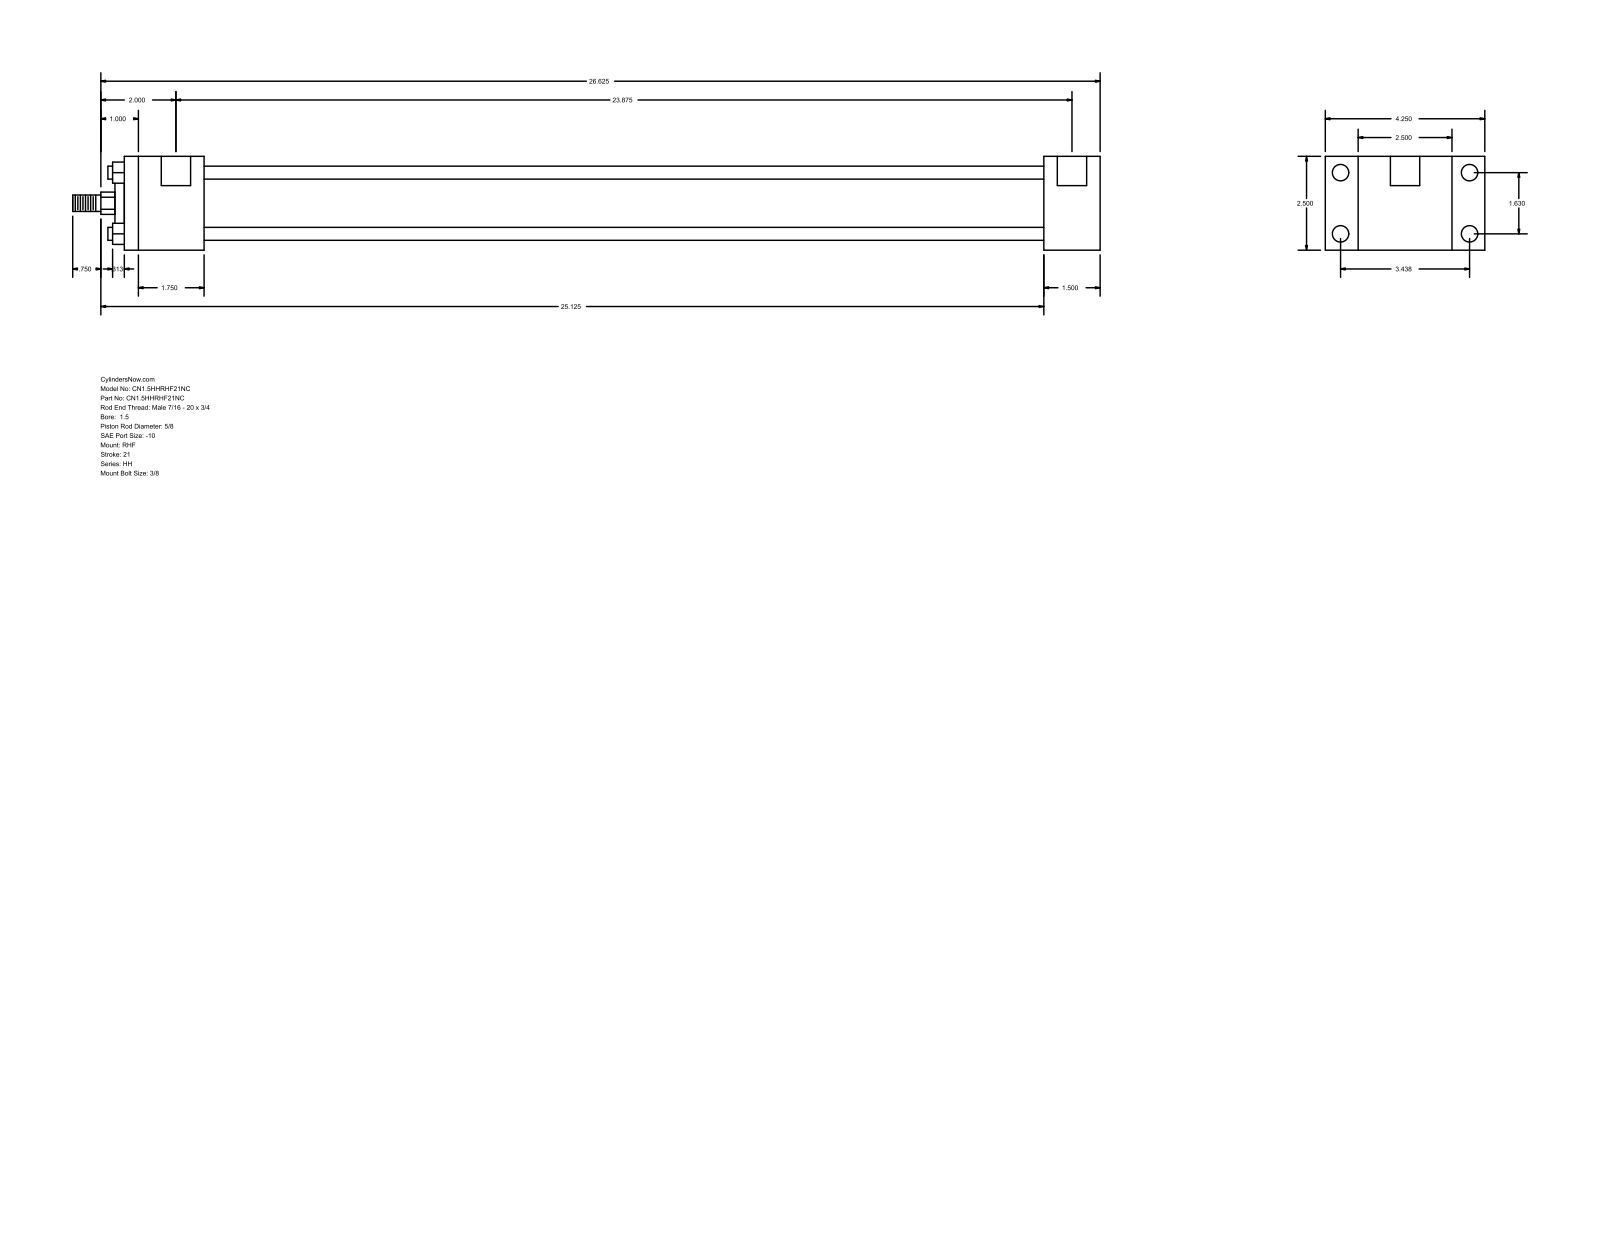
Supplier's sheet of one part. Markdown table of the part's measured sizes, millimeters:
| quantity | value |
| --- | --- |
| part name | HH_RHF__0150_0.625 |
| STEP written by | GSSL Pune (CONFIG_CONTROL_DESIGN) |
| units | millimeters |
| bodies | 0 solids, 88 faces (60 planar, 28 cylindrical, 0 other) |
| overall size | 695.33 × 107.95 × 63.5 |
| round holes (diameter × count) | 5.56 × 4, 11.13 × 4, 19.84 × 2 |
| round bosses / shafts (diameter × count) | 8.76 × 4, 44.45 × 1, 28.57 × 1, 15.88 × 1, 11.11 × 1 |
| partial cylindrical surfaces (radius × count) | 7.54 × 1 |
| main face-to-face distances | 63.5, 38.1, 22.23, 85.73, 622.29, 660.39, 107.96, 53.97, 568.32, 606.42 |
| hole center spacings | 41.4, 87.32, 96.64, 609.6, 1.58, 1.59, 606.43, 608.01 |
